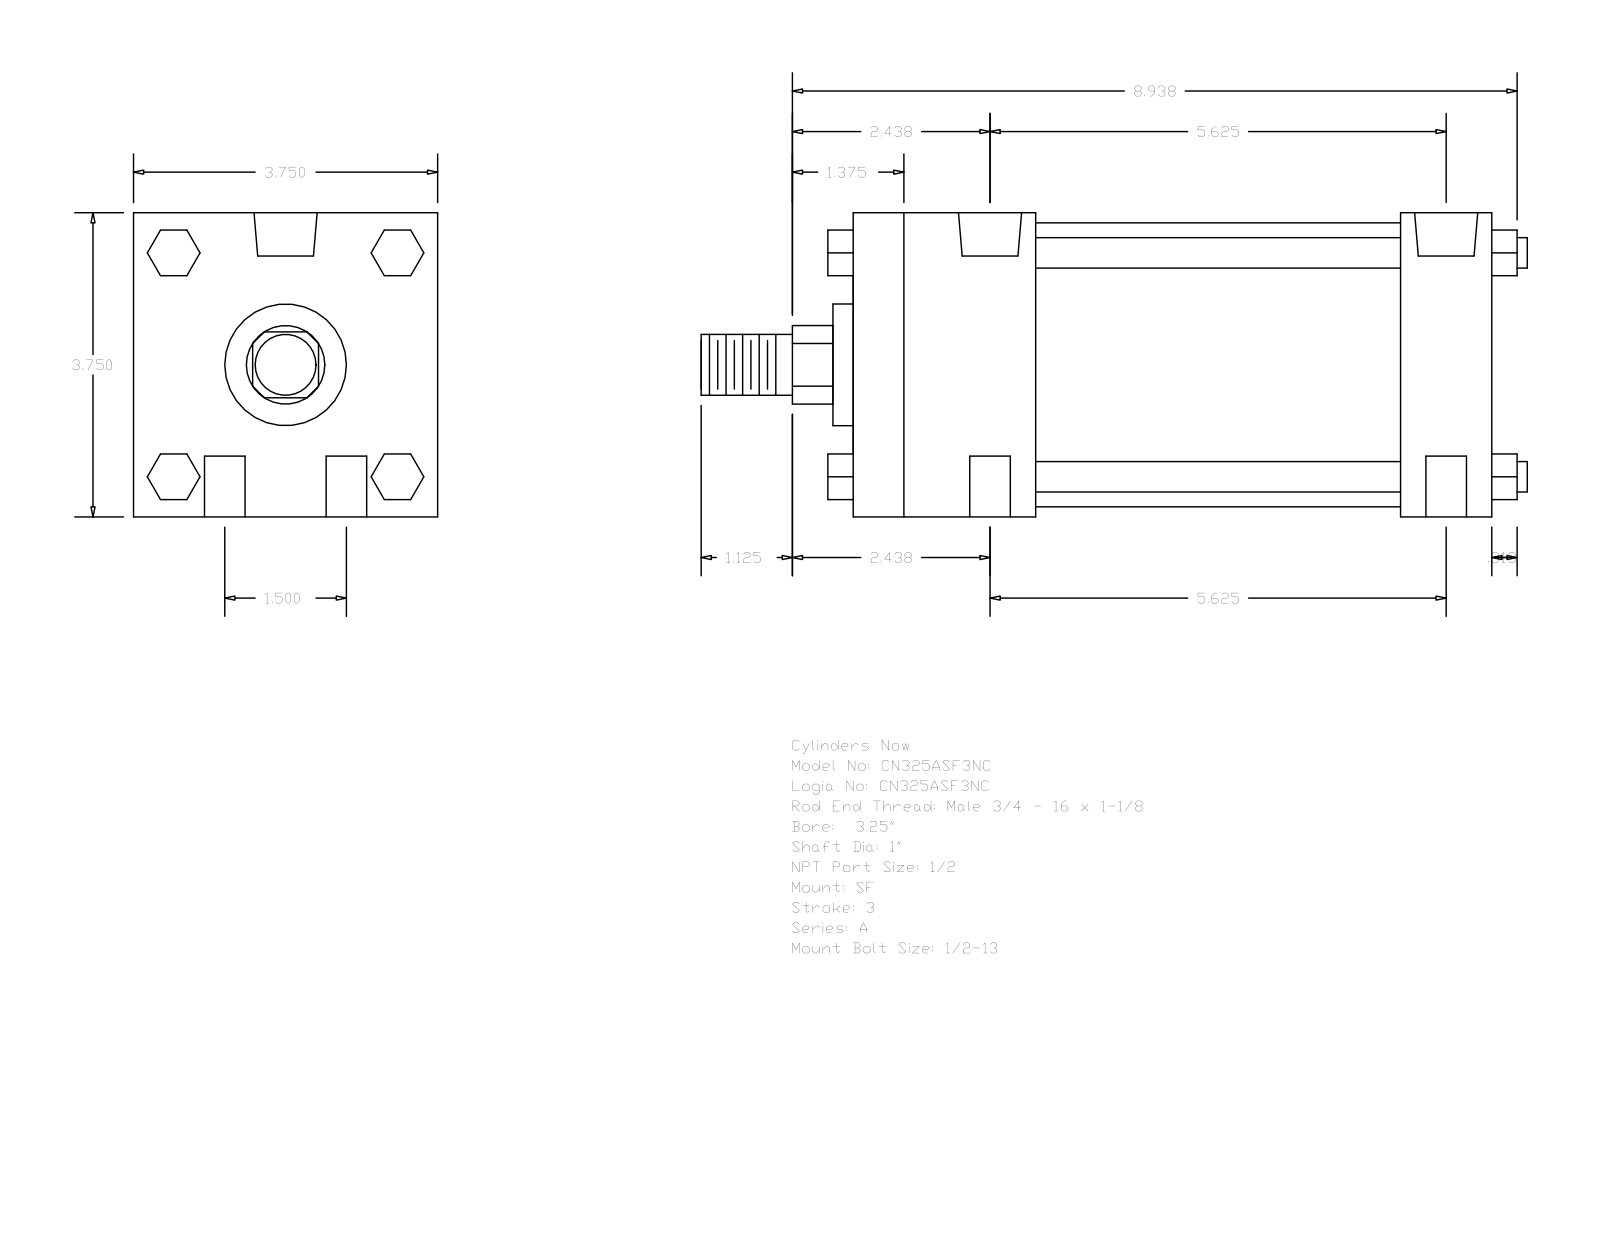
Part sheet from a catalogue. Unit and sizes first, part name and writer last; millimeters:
Units: millimetres
Overall size (bounding box): 258.76 × 95.25 × 95.25
Round holes (diameter × count): ⌀12.7 ×4, ⌀8.73 ×2, ⌀19.77 ×2
Round bosses / shafts (diameter × count): ⌀9.53 ×4, ⌀88.9 ×1, ⌀38.1 ×1, ⌀25.4 ×1, ⌀19.05 ×1
Partial cylindrical surfaces — rounded edges, fillets, slot ends (radius × count): R12.29 ×1
Main face-to-face distances: 95.24, 200.02, 28.57, 171.45, 57.15, 114.3, 142.87, 14.28, 35.05, 60.71
Hole centre spacings: 19.05, 144.14, 142.88, 38.1, 147.87, 136.52
Bodies: 0 solids, 124 faces (94 planar, 30 cylindrical, 0 other)
Part name (STEP PRODUCT): A_SF__0325_1
STEP written by: GSSL Pune (CONFIG_CONTROL_DESIGN)
